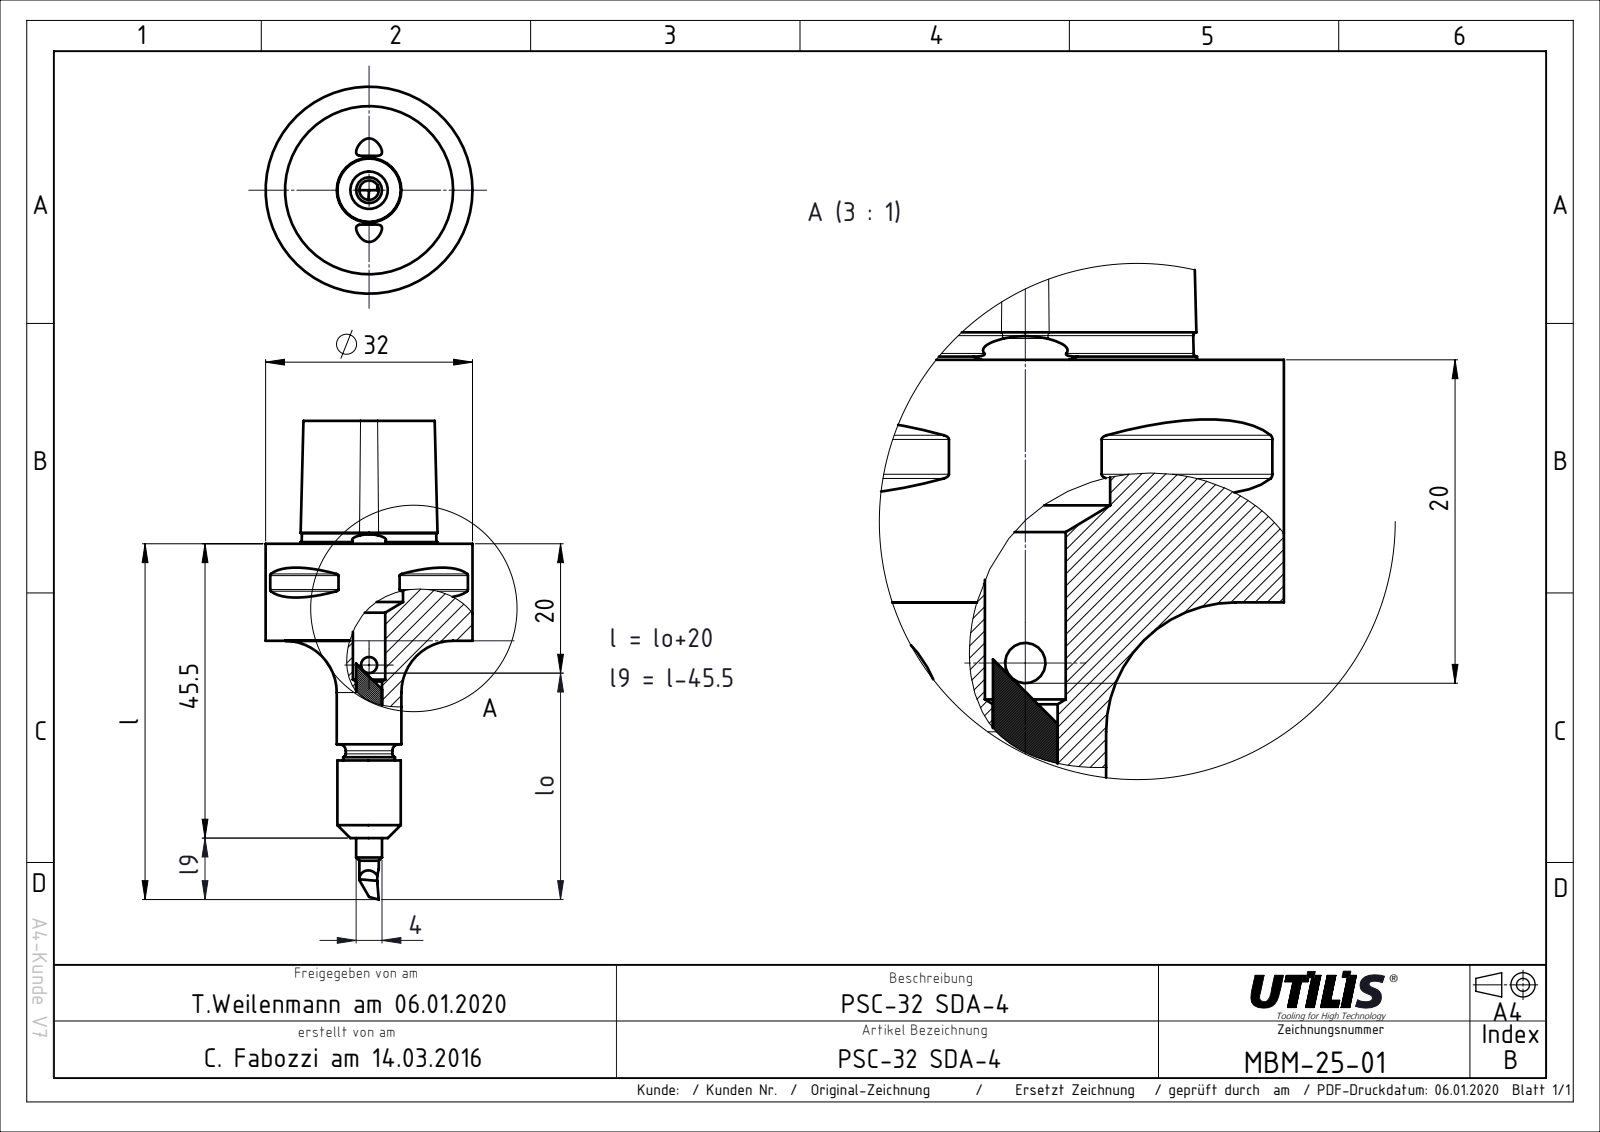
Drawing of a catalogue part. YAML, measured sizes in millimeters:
part_name: "MBM-25 PSC32_SDA4"
step_written_by: "SolidWorks 2015 (AUTOMOTIVE_DESIGN)"
units: millimeters
bodies: {solids: 1, faces: 135, planar: 28, cylindrical: 31, other: 76}
overall_size: [74, 32, 32]
volume: 19225
surface_area: 5854
round_holes:
  - {diameter: 3.6, count: 1}
  - {diameter: 15, count: 1}
  - {diameter: 16.5, count: 1}
round_bosses_or_shafts:
  - {diameter: 32, count: 1}
  - {diameter: 26, count: 1}
  - {diameter: 10, count: 1}
  - {diameter: 9.8, count: 1}
  - {diameter: 8, count: 1}
  - {diameter: 7.2, count: 1}
  - {diameter: 4, count: 1}
  - {diameter: 3, count: 1}
partial_cylinders:
  - {radius: 0.3, count: 8}
  - {radius: 3, count: 1}
face_to_face_distances: [15, 19, 34, 12.01, 28.3, 52.5, 33.5, 18.5, 64.5, 45.5]
